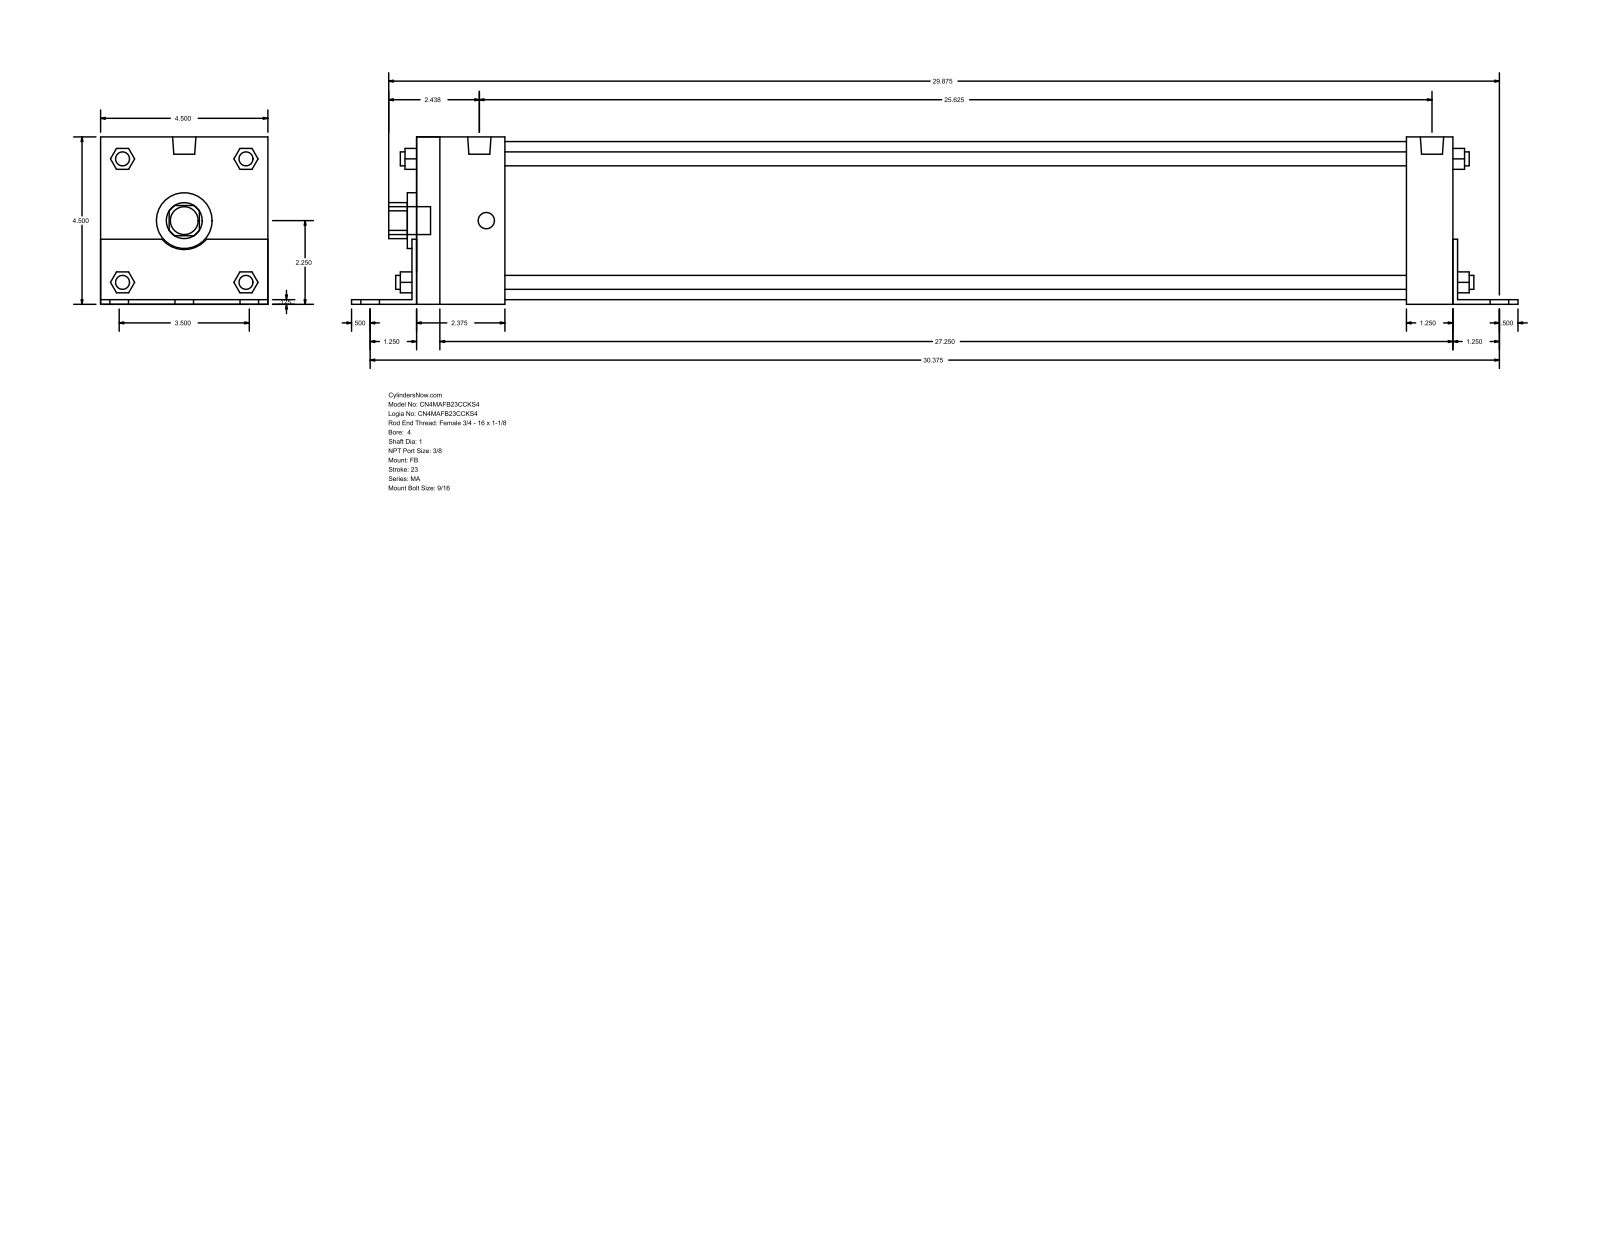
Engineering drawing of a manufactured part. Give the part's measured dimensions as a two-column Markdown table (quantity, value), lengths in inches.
| quantity | value |
| --- | --- |
| part name | MA_FB__0400_1 |
| STEP written by | GSSL Pune (CONFIG_CONTROL_DESIGN) |
| units | inches |
| bodies | 0 solids, 140 faces (105 planar, 35 cylindrical, 0 other) |
| overall size | 31.375 × 4.502 × 4.5 |
| round holes (diameter × count) | 1 × 1, 1.5 × 1, 4.25 × 1 |
| round bosses / shafts (diameter × count) | 0.563 × 6, 0.437 × 4, 0.375 × 4, 0.627 × 2, 0.75 × 1 |
| partial cylindrical surfaces (radius × count) | 0.484 × 1, 0.78 × 1 |
| main face-to-face distances | 4.5, 0.125, 4.502, 28, 0.123, 4.377, 27.875, 28.125, 26.75, 26.625 |
